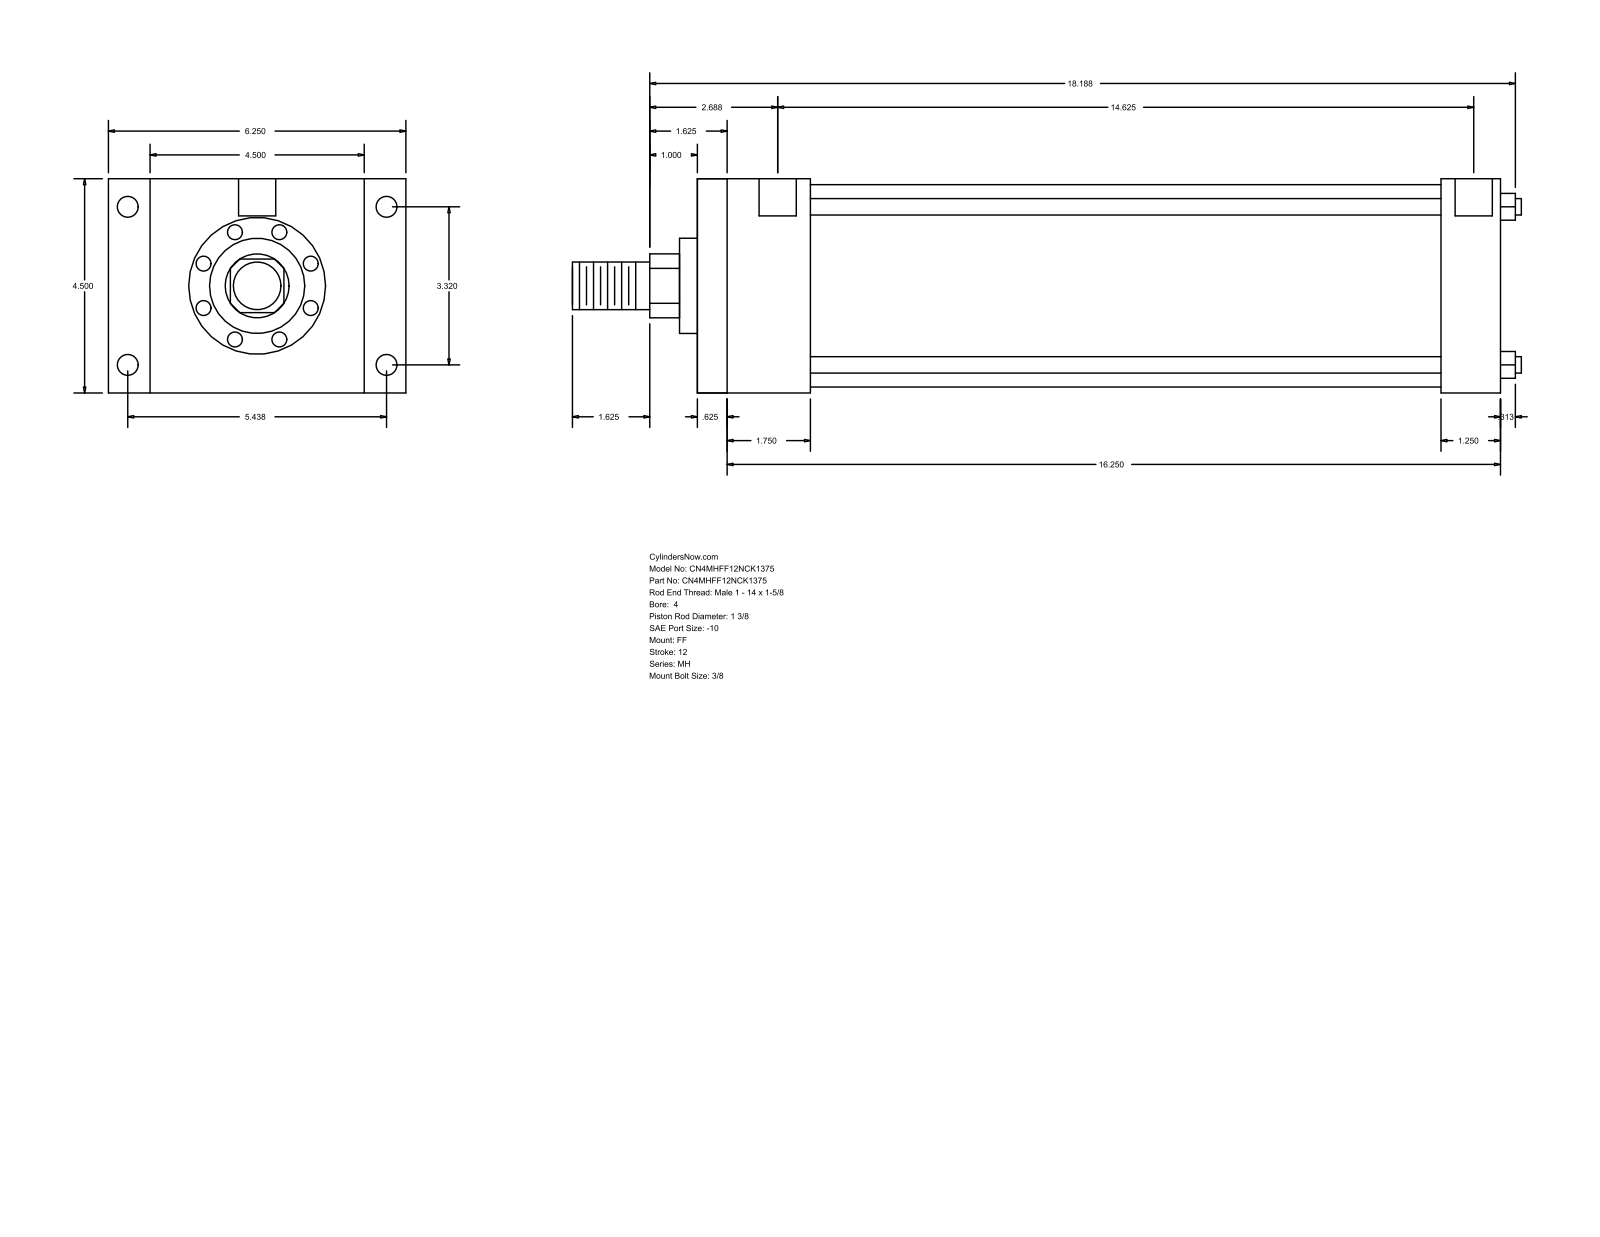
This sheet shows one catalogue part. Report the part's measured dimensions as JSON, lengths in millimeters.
{"part_name": "MH_FF__0400_1.375", "step_written_by": "GSSL Pune (CONFIG_CONTROL_DESIGN)", "units": "millimeters", "bodies": {"solids": 0, "faces": 92, "planar": 64, "cylindrical": 28, "other": 0}, "overall_size": [506.41, 158.75, 114.3], "round_holes": [[8.73, 4], [11.13, 4], [19.84, 2]], "round_bosses_or_shafts": [[8.76, 4], [107.95, 1], [50.8, 1], [34.92, 1], [25.4, 1]], "partial_cylinders_radius": [[17.06, 1]], "face_to_face_distances": [114.3, 428.62, 15.87, 412.75, 60.32, 44.45, 368.3, 396.87, 381, 336.55], "hole_center_spacings": [84.32, 138.12, 161.82, 374.65, 1.58, 1.59, 371.48, 373.06]}
